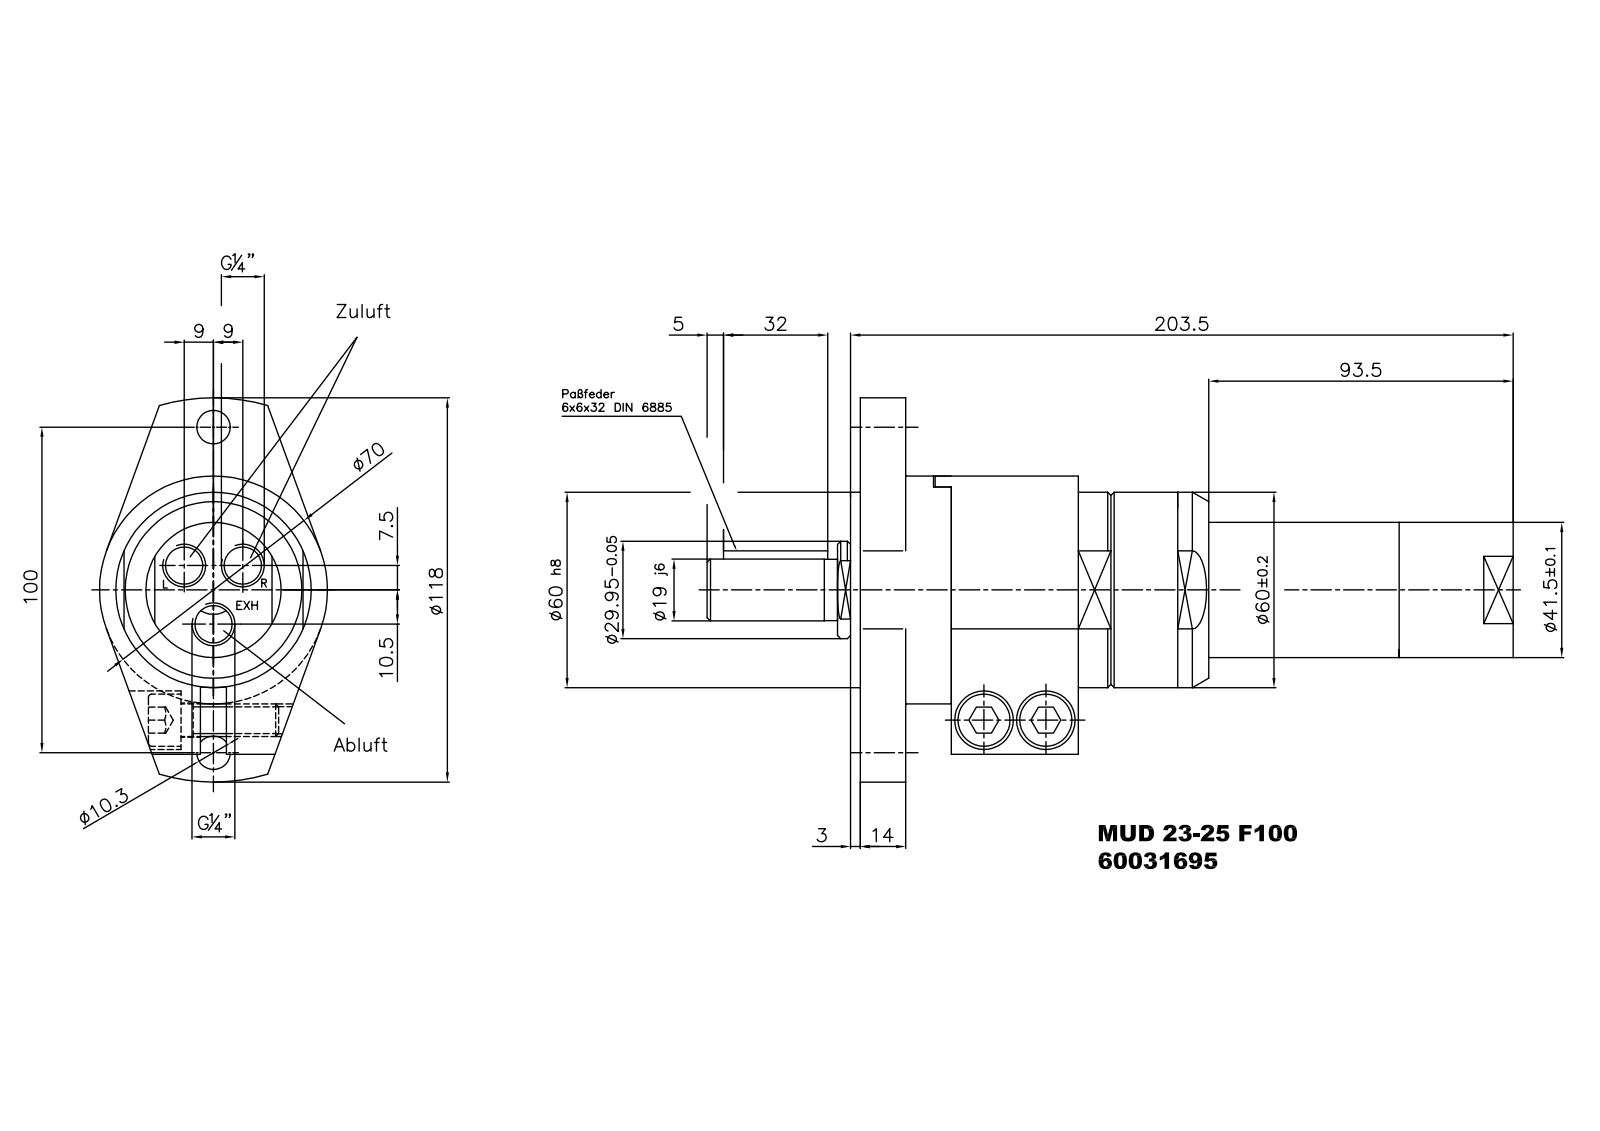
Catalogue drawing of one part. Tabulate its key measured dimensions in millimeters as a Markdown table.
| quantity | value |
| --- | --- |
| part name | MUD 23- 203,5 F100 |
| STEP written by | Autodesk Inventor 2013 (CONFIG_CONTROL_DESIGN) |
| units | millimeters |
| bodies | 1 solid, 203 faces (127 planar, 48 cylindrical, 28 other) |
| overall size | 247.5 × 118 × 70 |
| volume | 564 457 mm³ |
| surface area | 75 195 mm² |
| round holes (diameter × count) | 11.45 × 3, 8.38 × 2, 10.3 × 2, 10.5 × 2, 18 × 2, 1.6 × 1, 20 × 1, 35 × 1, 42 × 1, 44 × 1, 52.1 × 1, 57.01 × 1 |
| round bosses / shafts (diameter × count) | 16 × 2, 10 × 2, 70 × 1, 60 × 1, 57 × 1, 55.16 × 1, 52 × 1, 41.5 × 1 |
| partial cylindrical surfaces (radius × count) | 3 × 2, 59 × 1 |
| main face-to-face distances | 14, 17, 97.5, 3, 9.5, 70.1, 67.1, 53.1, 100.5, 83.5 |
| hole center spacings | 11.72, 20.12, 43.44, 50, 58.2, 10.5, 18, 19 |
